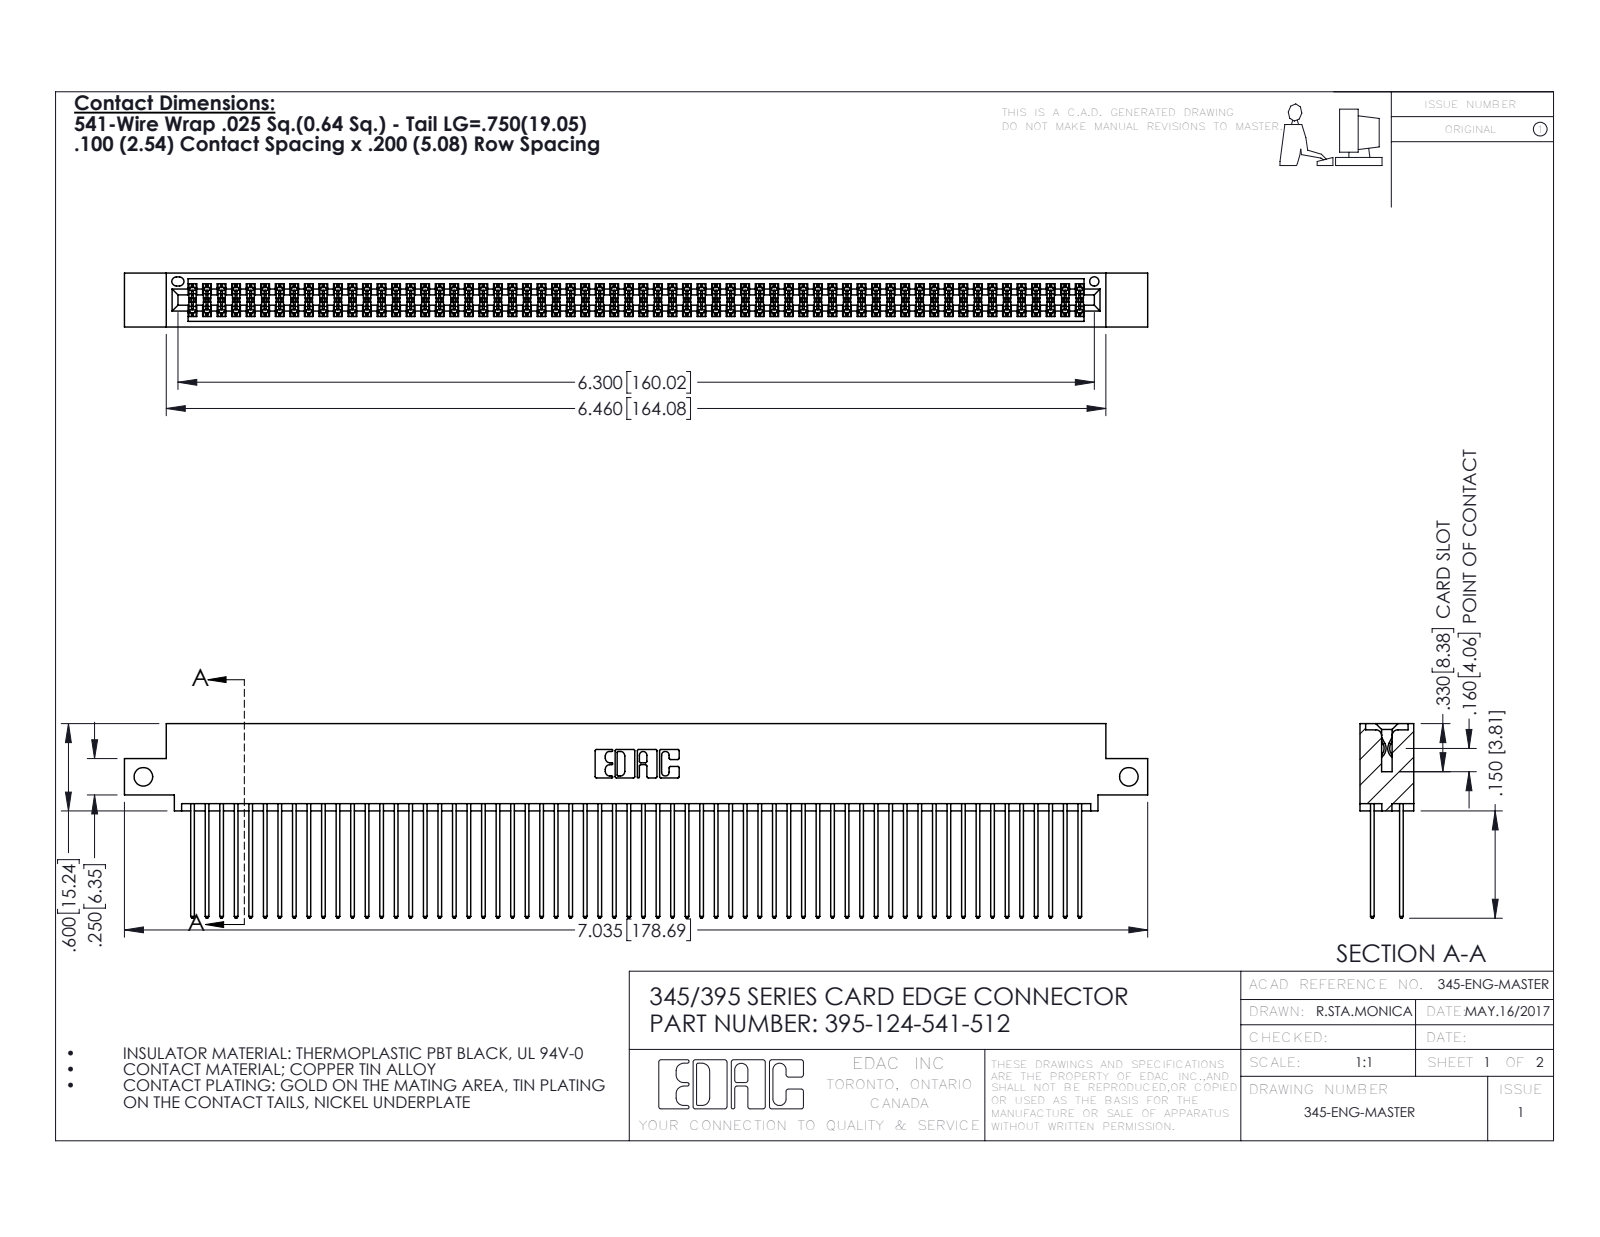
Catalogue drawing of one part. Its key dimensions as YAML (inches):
part_name: "395-124-541-512; 345 Part_0.110 Offset - Side Mount; 345-292-001_345-293-141"
step_written_by: "SolidWorks 2016 (CONFIG_CONTROL_DESIGN)"
units: inches
bodies: {solids: 125, faces: 6330, planar: 4176, cylindrical: 2154, other: 0}
overall_size: [7.035, 1.337, 0.37]
volume: 1.104
surface_area: 47.17
round_holes:
  - {diameter: 0.128, count: 2}
  - {diameter: 0.064, count: 1}
partial_cylinders:
  - {radius: 0.006, count: 186}
  - {radius: 0.01, count: 124}
  - {radius: 0.01, count: 22}
  - {radius: 0.007, count: 6}
  - {radius: 0.031, count: 6}
  - {radius: 0.026, count: 3}
  - {radius: 0.014, count: 2}
  - {radius: 0.019, count: 2}
face_to_face_distances: [0.072, 0.298, 0.2, 0.098, 0.272, 0.025, 0.225, 0.37, 0.175, 0.149]
hole_center_spacings: [6.775]
